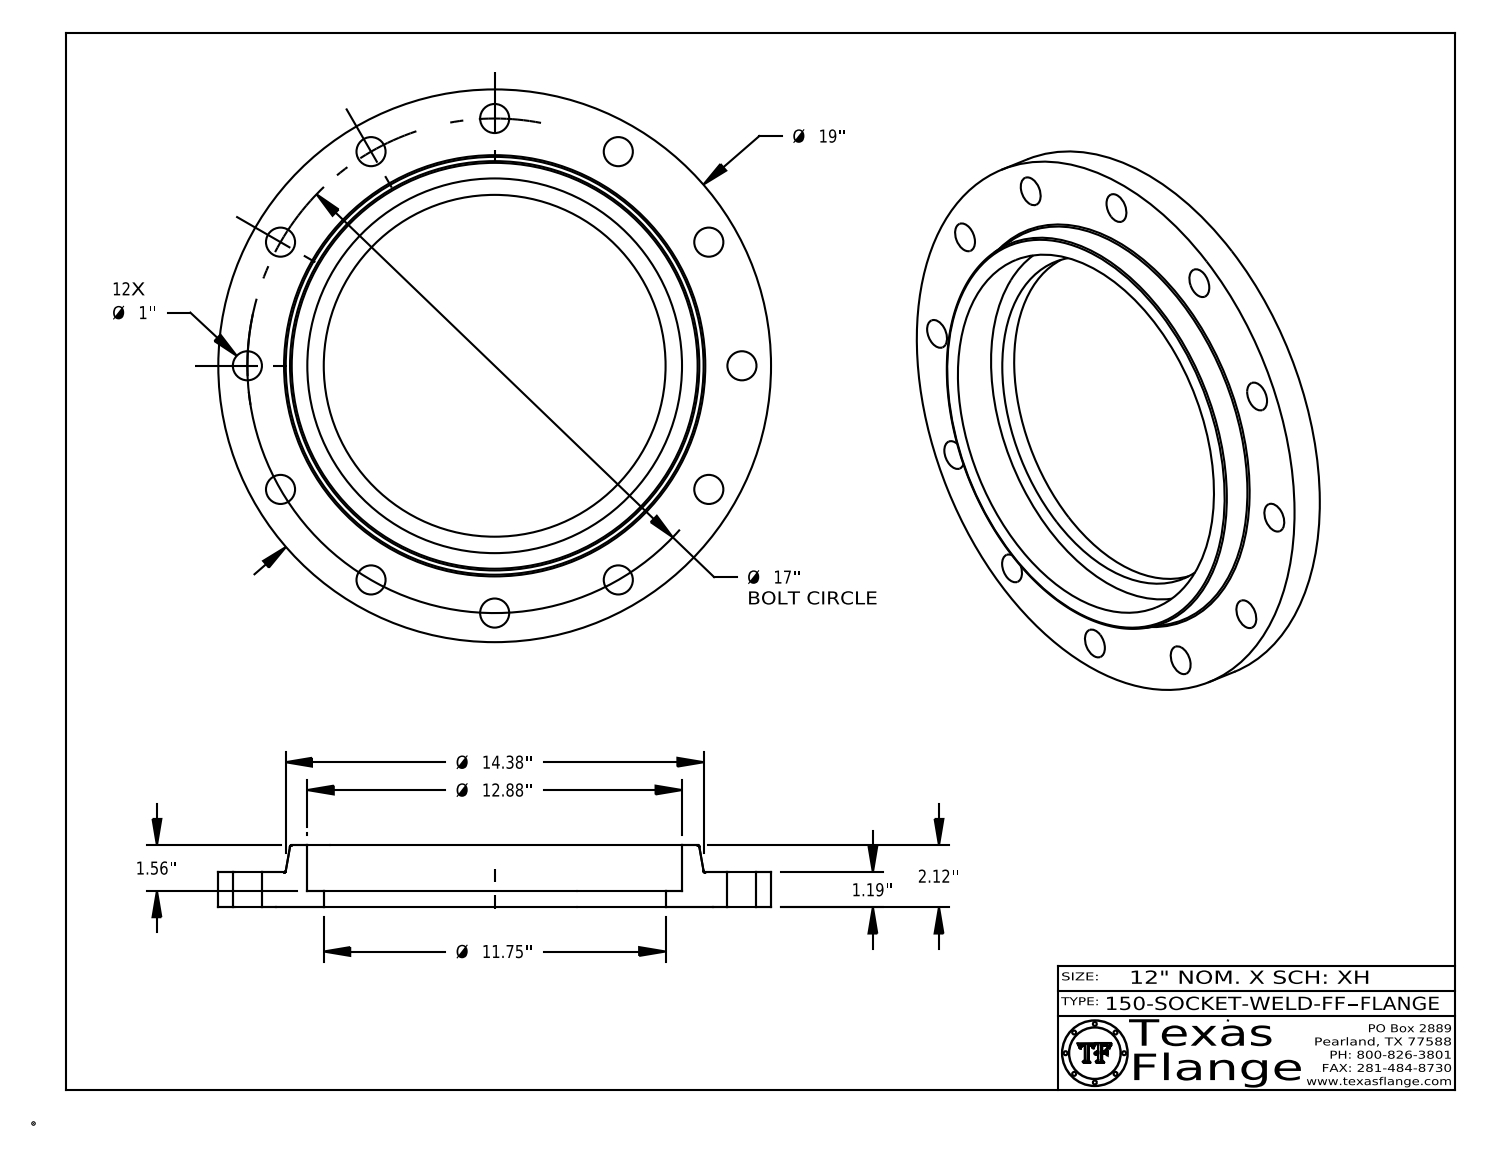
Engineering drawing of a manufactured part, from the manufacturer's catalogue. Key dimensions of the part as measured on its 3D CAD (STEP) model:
Part name (STEP PRODUCT): 150-SOCKET-WELD-FF
STEP written by: CATIA V5 STEP AP214 (AUTOMOTIVE_DESIGN)
Units: inches
Bodies: 1 solid, 426 faces (370 planar, 50 cylindrical, 6 other)
Overall size (bounding box): 19 × 19 × 2.12
Volume: 209.8 in³ · Surface area: 564.5 in²
Round holes (diameter × count): ⌀1 ×12, ⌀0.495 ×1, ⌀11.75 ×1, ⌀12.88 ×1
Round bosses / shafts (diameter × count): ⌀0.03 ×8, ⌀19 ×1, ⌀0.39 ×1
Main face-to-face distances: 1.19, 2.12, 0.93, 0.56, 0.63, 1.56, 0.015, 1.175, 0.615, 0.945
Hole centre spacings: 8.5, 16.42, 4.4, 12.02, 14.722, 4.4, 12.021, 14.722
